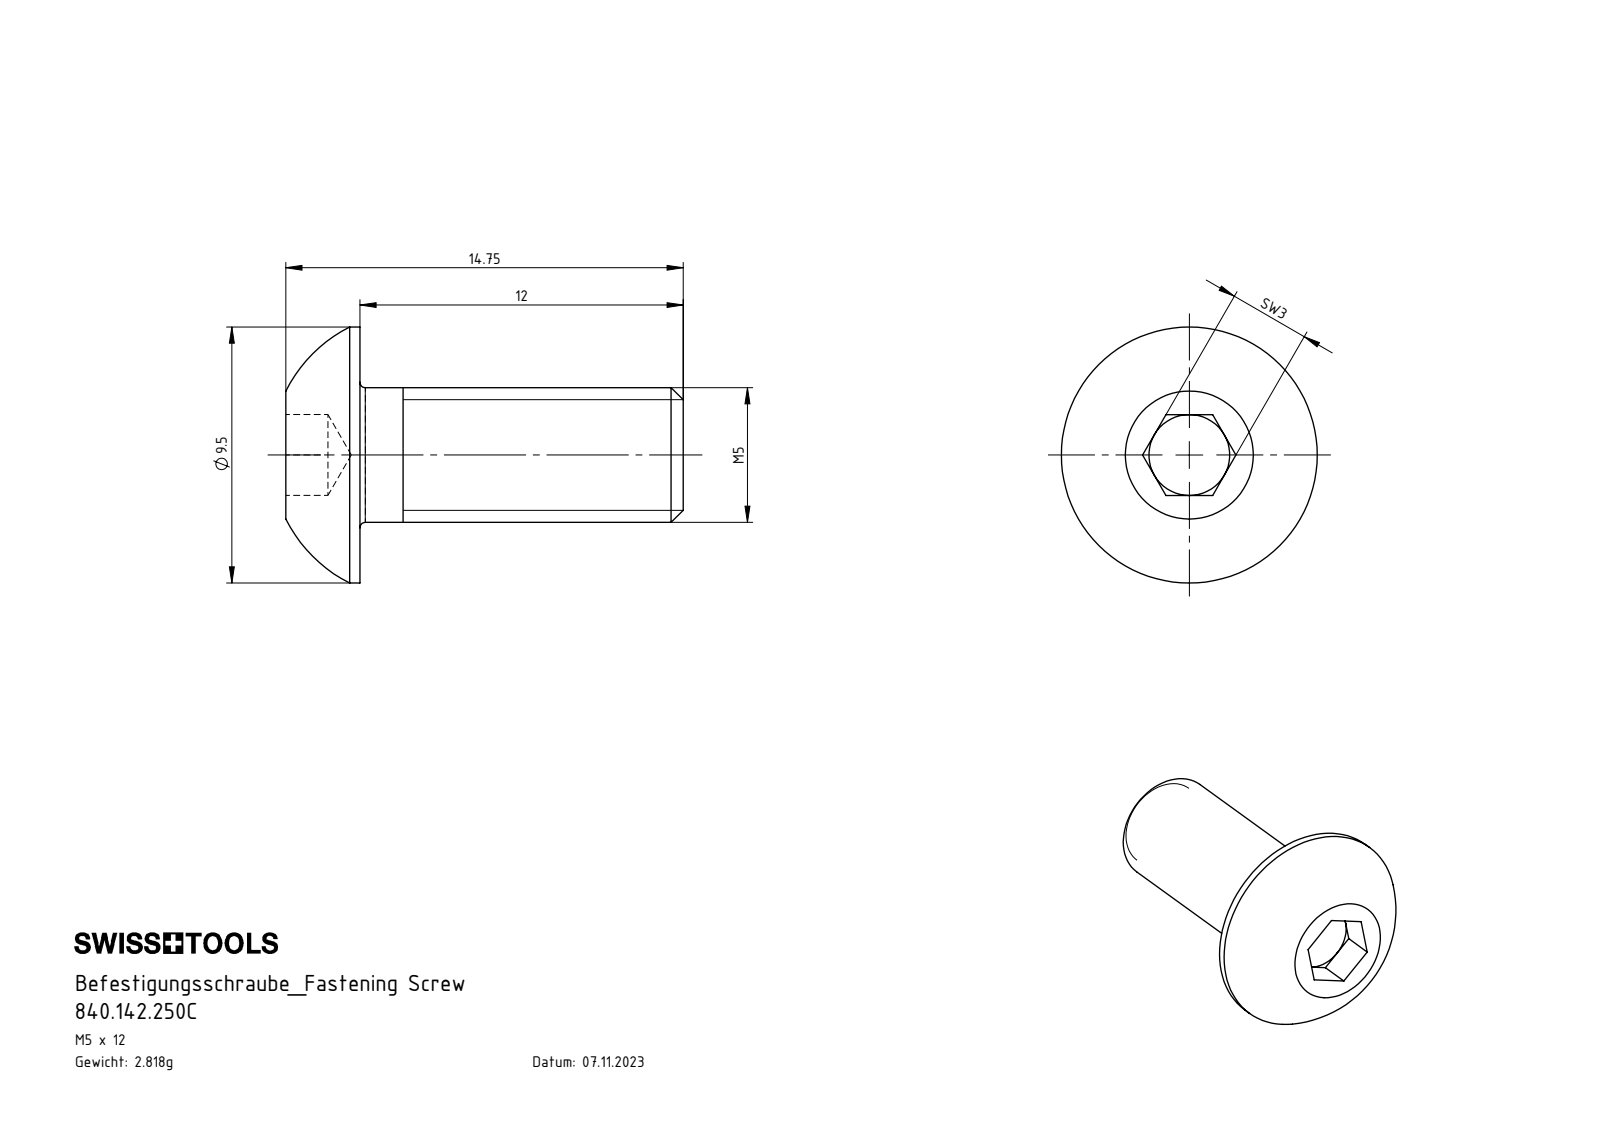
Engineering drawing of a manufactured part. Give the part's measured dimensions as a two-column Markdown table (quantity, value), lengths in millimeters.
| quantity | value |
| --- | --- |
| part name | 840.142.250C |
| STEP written by | SolidWorks 2022 (AUTOMOTIVE_DESIGN) |
| units | millimeters |
| bodies | 1 solid, 27 faces (15 planar, 4 cylindrical, 8 other) |
| overall size | 14.75 × 9.5 × 9.5 |
| volume | 359 mm³ |
| surface area | 379 mm² |
| round bosses / shafts (diameter × count) | 9.5 × 1, 5 × 1 |
| main face-to-face distances | 12, 2.75, 14.75, 3, 1.56, 1.19, 13.19 |
